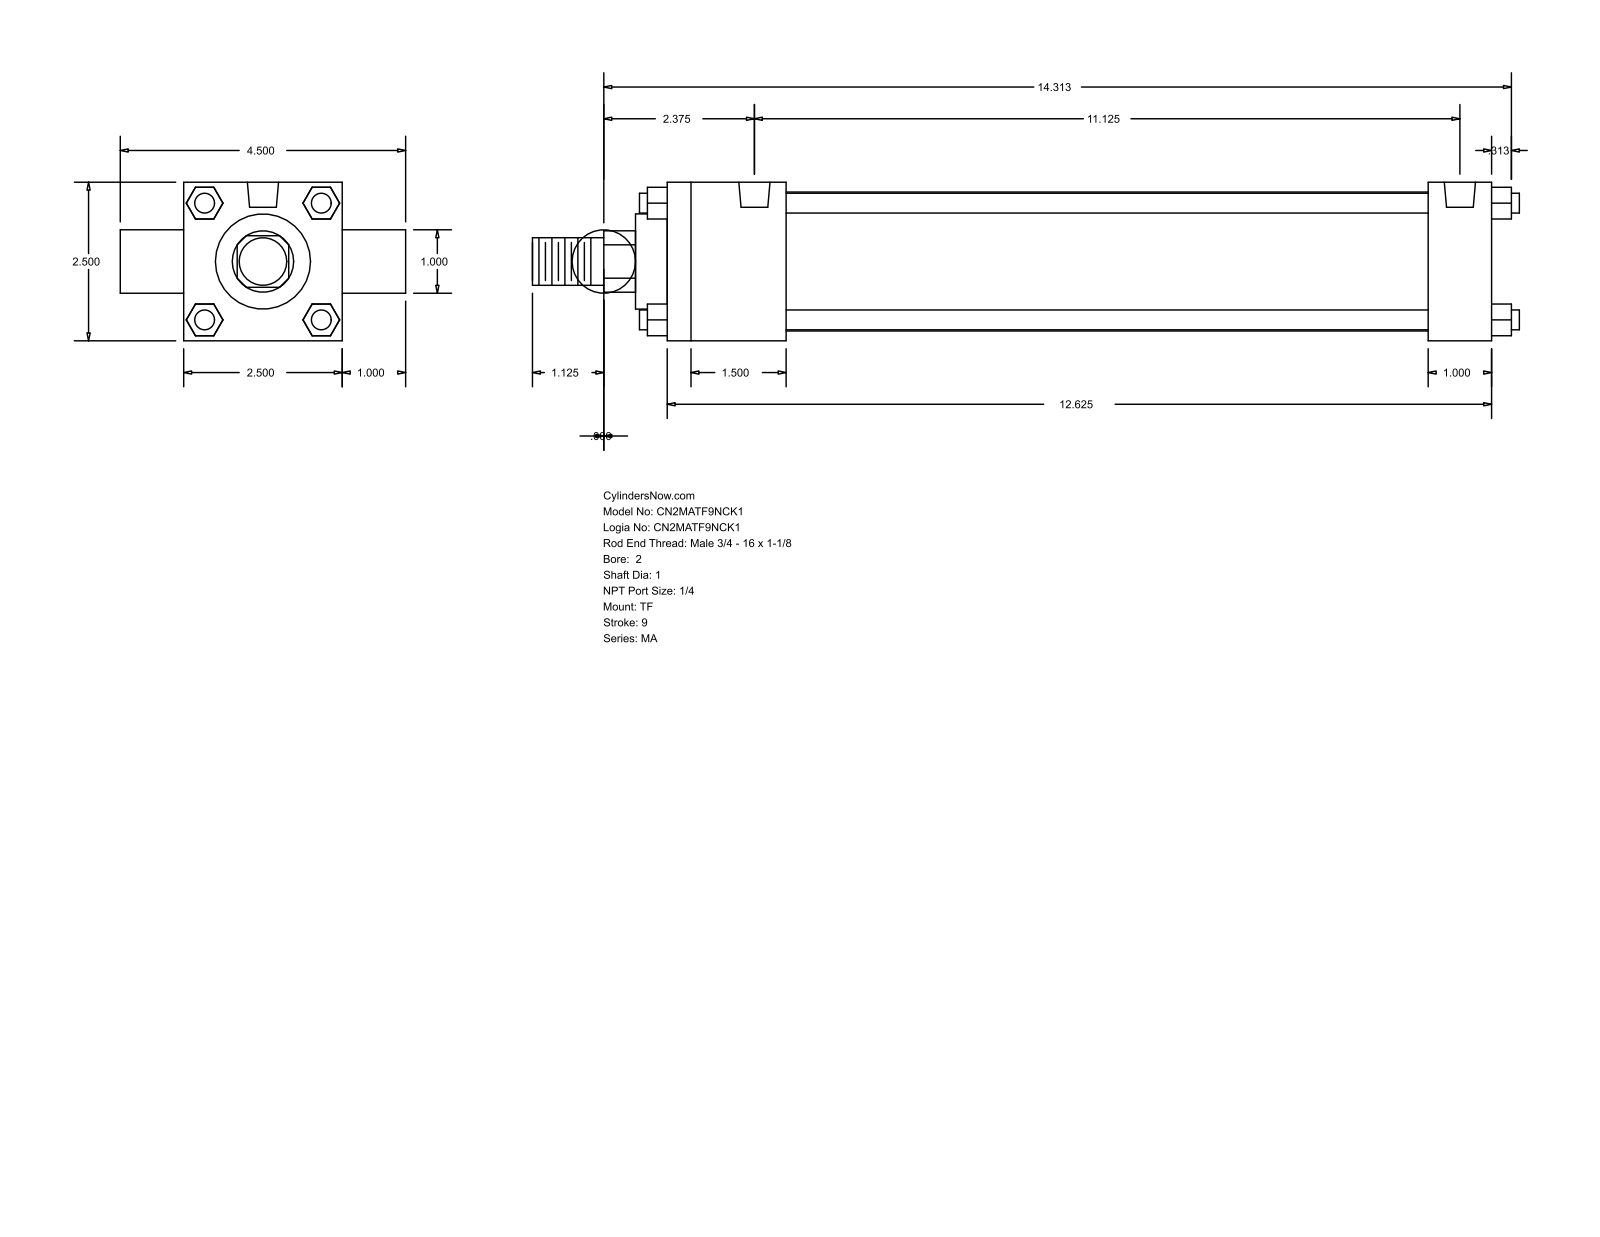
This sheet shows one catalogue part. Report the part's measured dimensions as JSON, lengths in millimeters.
{"part_name": "MA_TF__0200_1", "step_written_by": "GSSL Pune (CONFIG_CONTROL_DESIGN)", "units": "millimeters", "bodies": {"solids": 0, "faces": 120, "planar": 92, "cylindrical": 28, "other": 0}, "overall_size": [395.29, 114.3, 63.5], "round_holes": [[7.94, 3], [12.49, 2]], "round_bosses_or_shafts": [[7.94, 4], [25.4, 2], [55.63, 1], [38.1, 1], [19.05, 1]], "partial_cylinders_radius": [[12.29, 1]], "face_to_face_distances": [63.5, 25.4, 330.2, 12.7, 47.63, 304.8, 257.17, 282.57, 88.9, 23.37], "hole_center_spacings": [282.57]}
